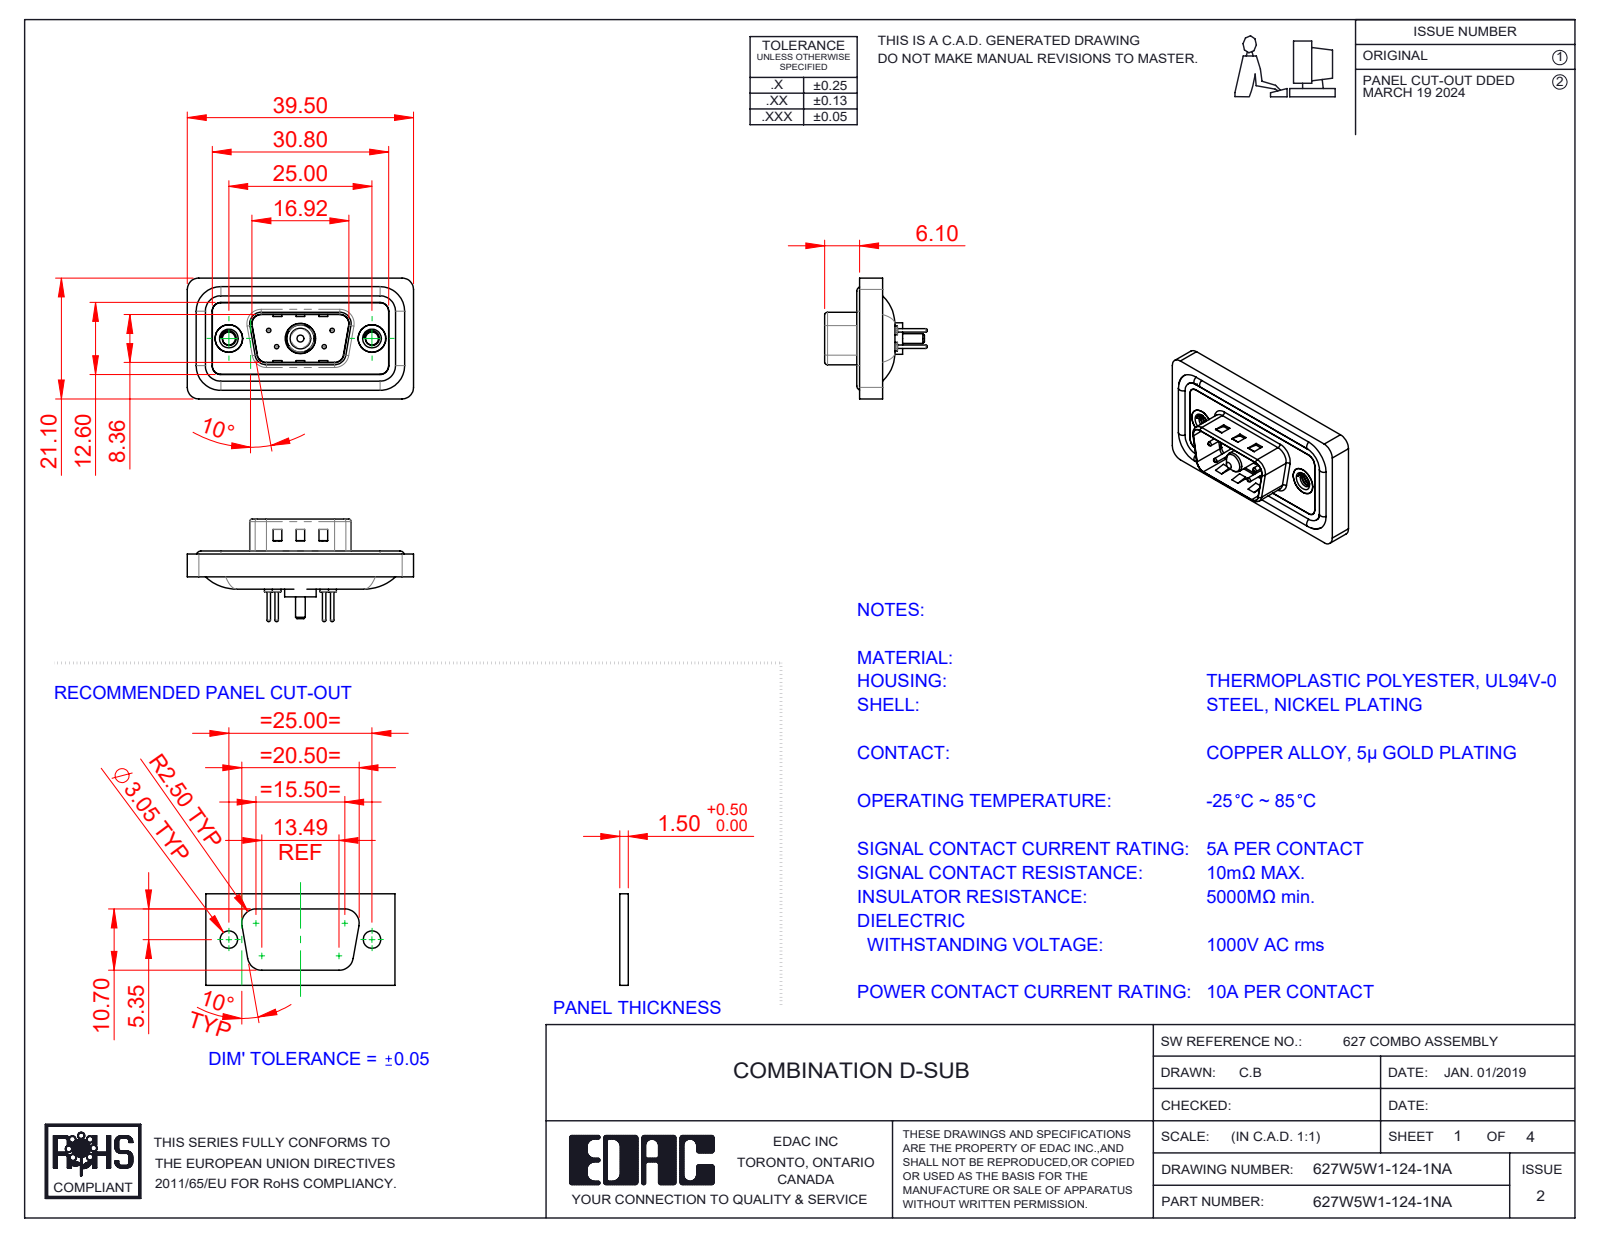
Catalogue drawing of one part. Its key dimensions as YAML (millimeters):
part_name: "627Combo Shell Rear_09 Contacts; 627Combo Contact Row 2_24; 627Combo Contact Row 1_24; 627Combo Shell Front_09 Contacts (+5 more)"
step_written_by: "SolidWorks 2023 (CONFIG_CONTROL_DESIGN)"
units: millimeters
bodies: {solids: 13, faces: 596, planar: 183, cylindrical: 257, other: 156}
overall_size: [39.5, 21.1, 17.9]
volume: 4374
surface_area: 6926
round_holes:
  - {diameter: 0.75, count: 4}
  - {diameter: 1.6, count: 4}
  - {diameter: 2, count: 4}
  - {diameter: 2.26, count: 2}
  - {diameter: 4, count: 2}
  - {diameter: 4.8, count: 2}
  - {diameter: 5, count: 2}
  - {diameter: 4.85, count: 1}
  - {diameter: 5.3, count: 1}
round_bosses_or_shafts:
  - {diameter: 1.6, count: 4}
  - {diameter: 1.5, count: 4}
  - {diameter: 0.6, count: 4}
  - {diameter: 4.9, count: 2}
  - {diameter: 5.5, count: 1}
  - {diameter: 5.2, count: 1}
  - {diameter: 4.75, count: 1}
  - {diameter: 3.75, count: 1}
partial_cylinders:
  - {radius: 1.5, count: 22}
  - {radius: 2, count: 18}
  - {radius: 0.5, count: 8}
  - {radius: 1.6, count: 8}
  - {radius: 0.25, count: 4}
  - {radius: 0.6, count: 4}
  - {radius: 0.65, count: 4}
  - {radius: 0.9, count: 4}
face_to_face_distances: [0.4, 1.1, 2.9, 1.6, 1.5, 3.1, 0.5, 2.5, 4, 0.8]
hole_center_spacings: [3.16, 5.72, 7.1, 12.5, 18.1, 4.39, 4.4, 8.31]
